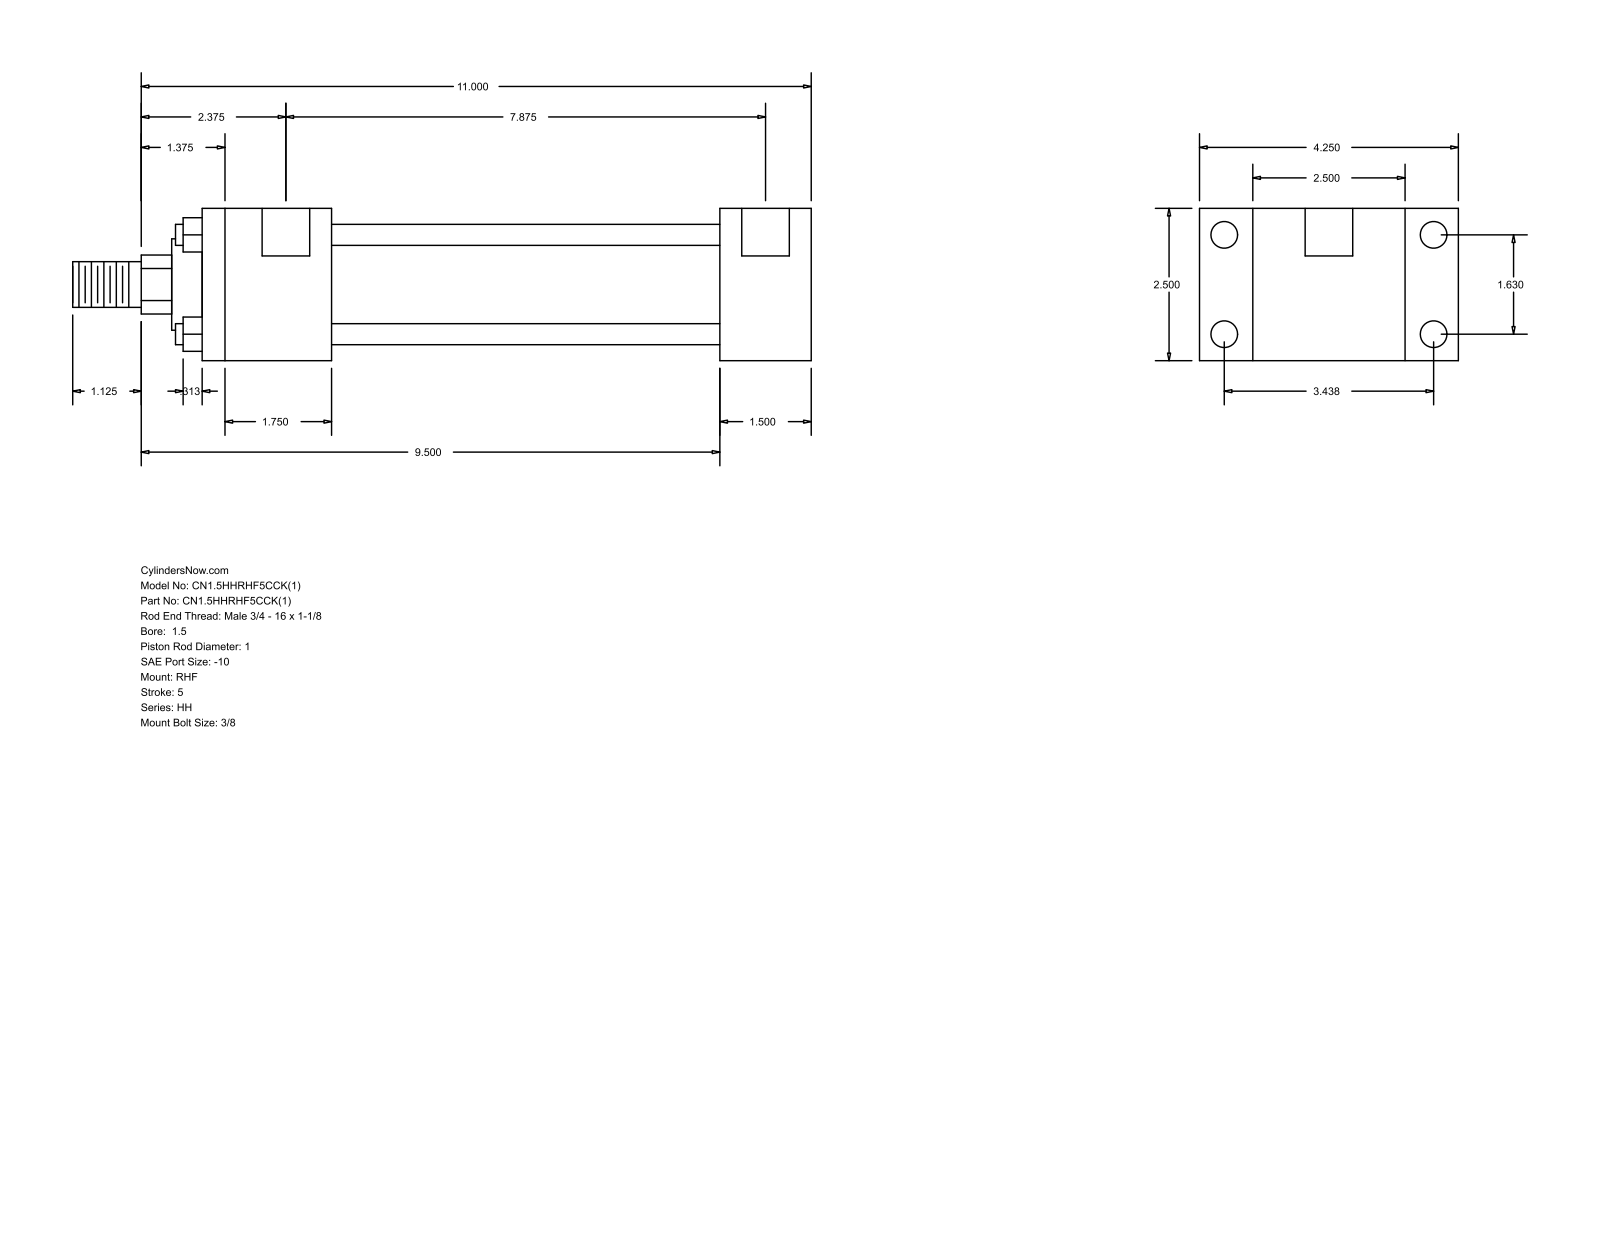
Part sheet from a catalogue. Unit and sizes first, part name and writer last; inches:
Units: inches
Overall size (bounding box): 12.125 × 4.25 × 2.5
Round holes (diameter × count): ⌀0.219 ×4, ⌀0.438 ×4, ⌀0.781 ×2
Round bosses / shafts (diameter × count): ⌀0.345 ×4, ⌀1.75 ×1, ⌀1.5 ×1, ⌀1 ×1, ⌀0.75 ×1
Partial cylindrical surfaces — rounded edges, fillets, slot ends (radius × count): R0.484 ×1
Main face-to-face distances: 2.5, 0.875, 3.375, 1.5, 4.25, 6.375, 7.875, 2.125, 8.5, 10
Hole centre spacings: 0.063, 1.63, 3.438, 3.805, 7.937, 8, 7.875
Bodies: 0 solids, 88 faces (60 planar, 28 cylindrical, 0 other)
Part name (STEP PRODUCT): HH_RHF__0150_1
STEP written by: GSSL Pune (CONFIG_CONTROL_DESIGN)
